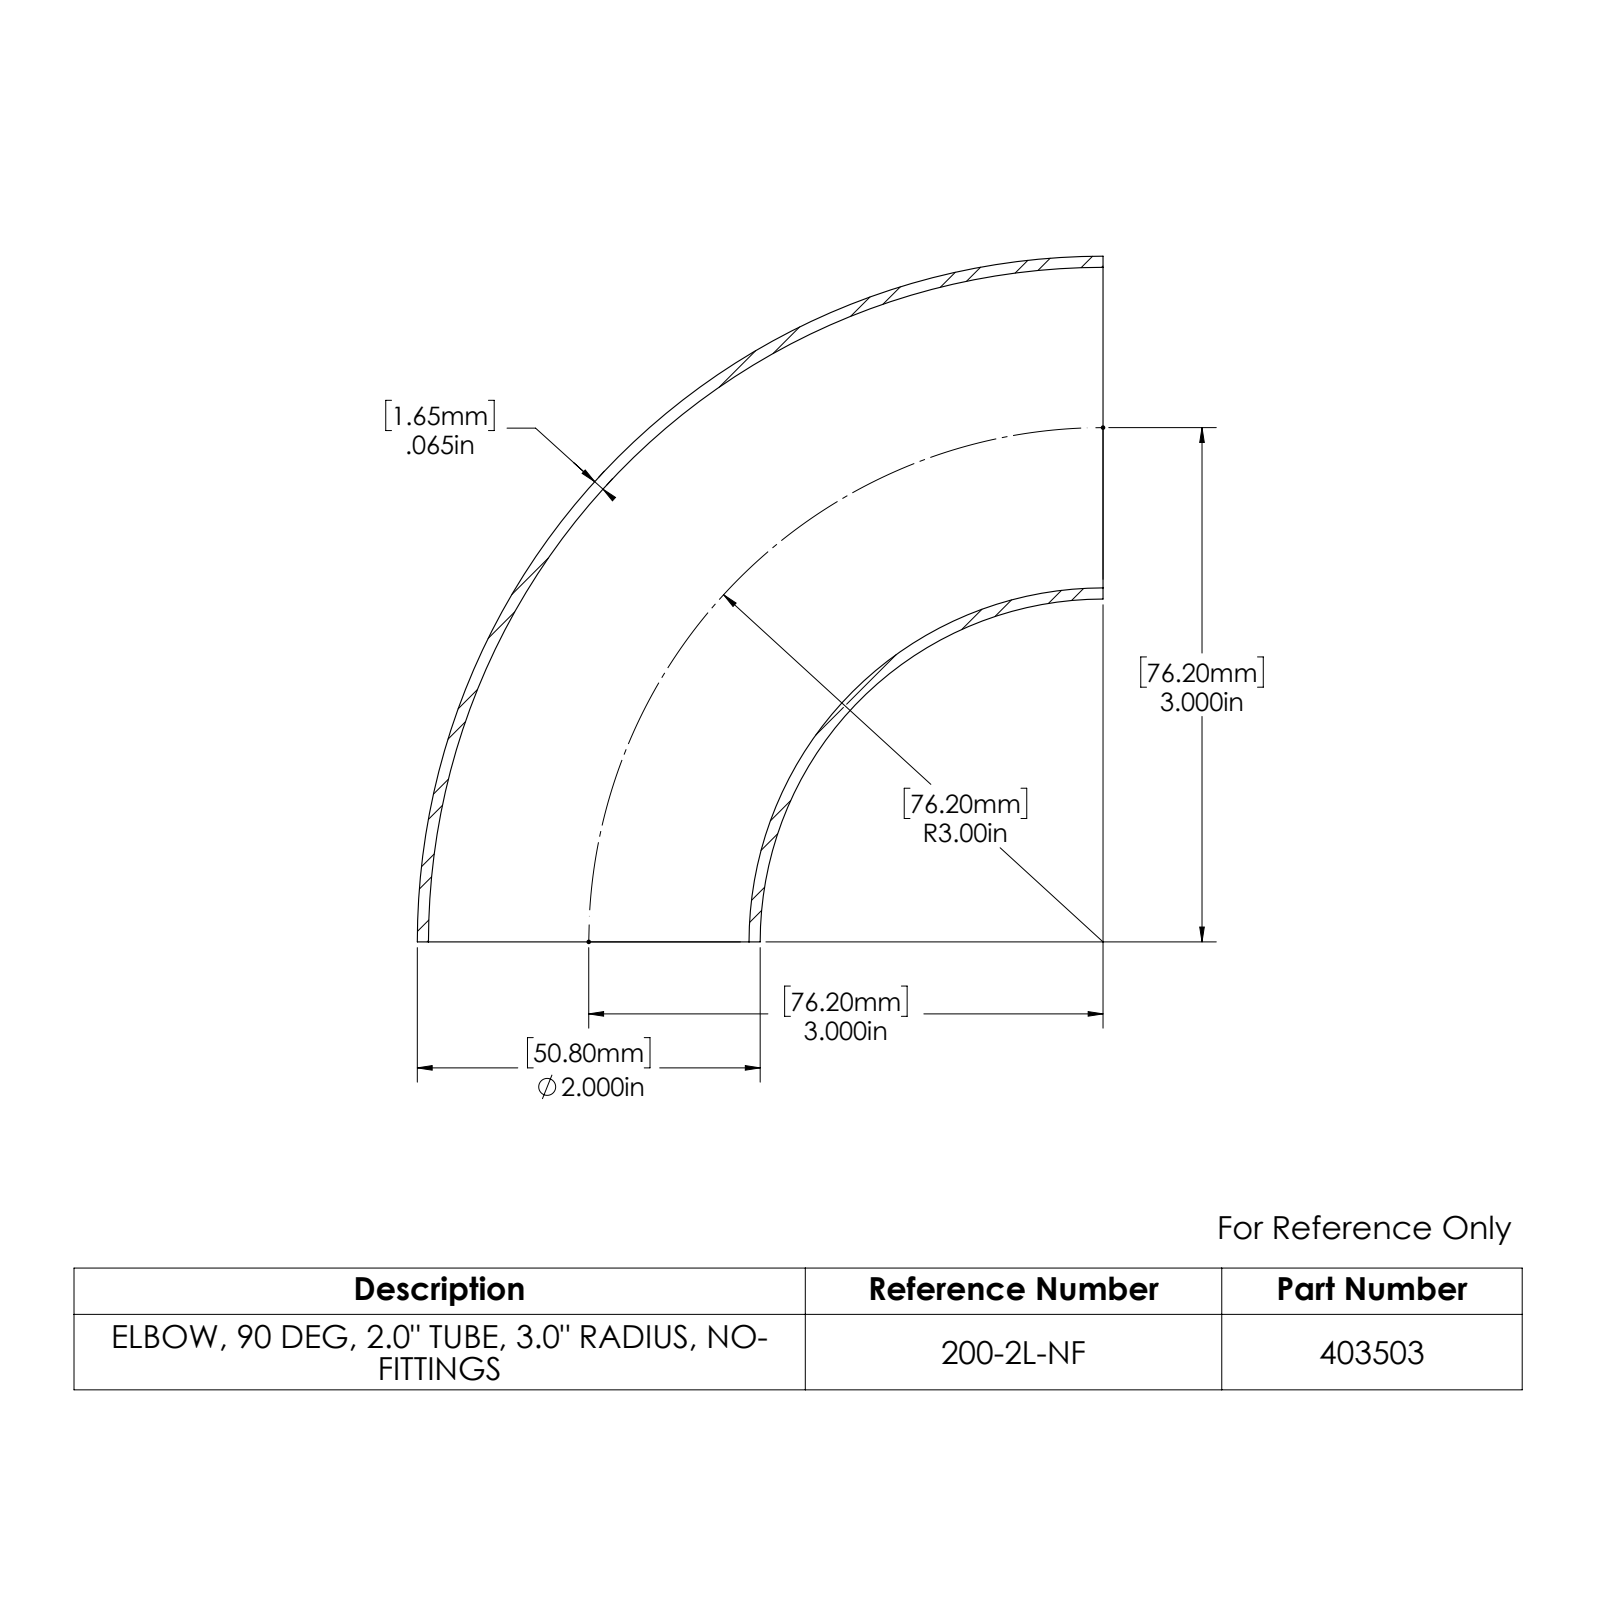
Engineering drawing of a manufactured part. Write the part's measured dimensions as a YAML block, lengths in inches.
part_name: "403503"
step_written_by: "SolidWorks 2022 (AUTOMOTIVE_DESIGN)"
units: inches
bodies: {solids: 1, faces: 6, planar: 2, cylindrical: 0, other: 4}
overall_size: [4, 4, 2]
volume: 1.862
surface_area: 58.08
